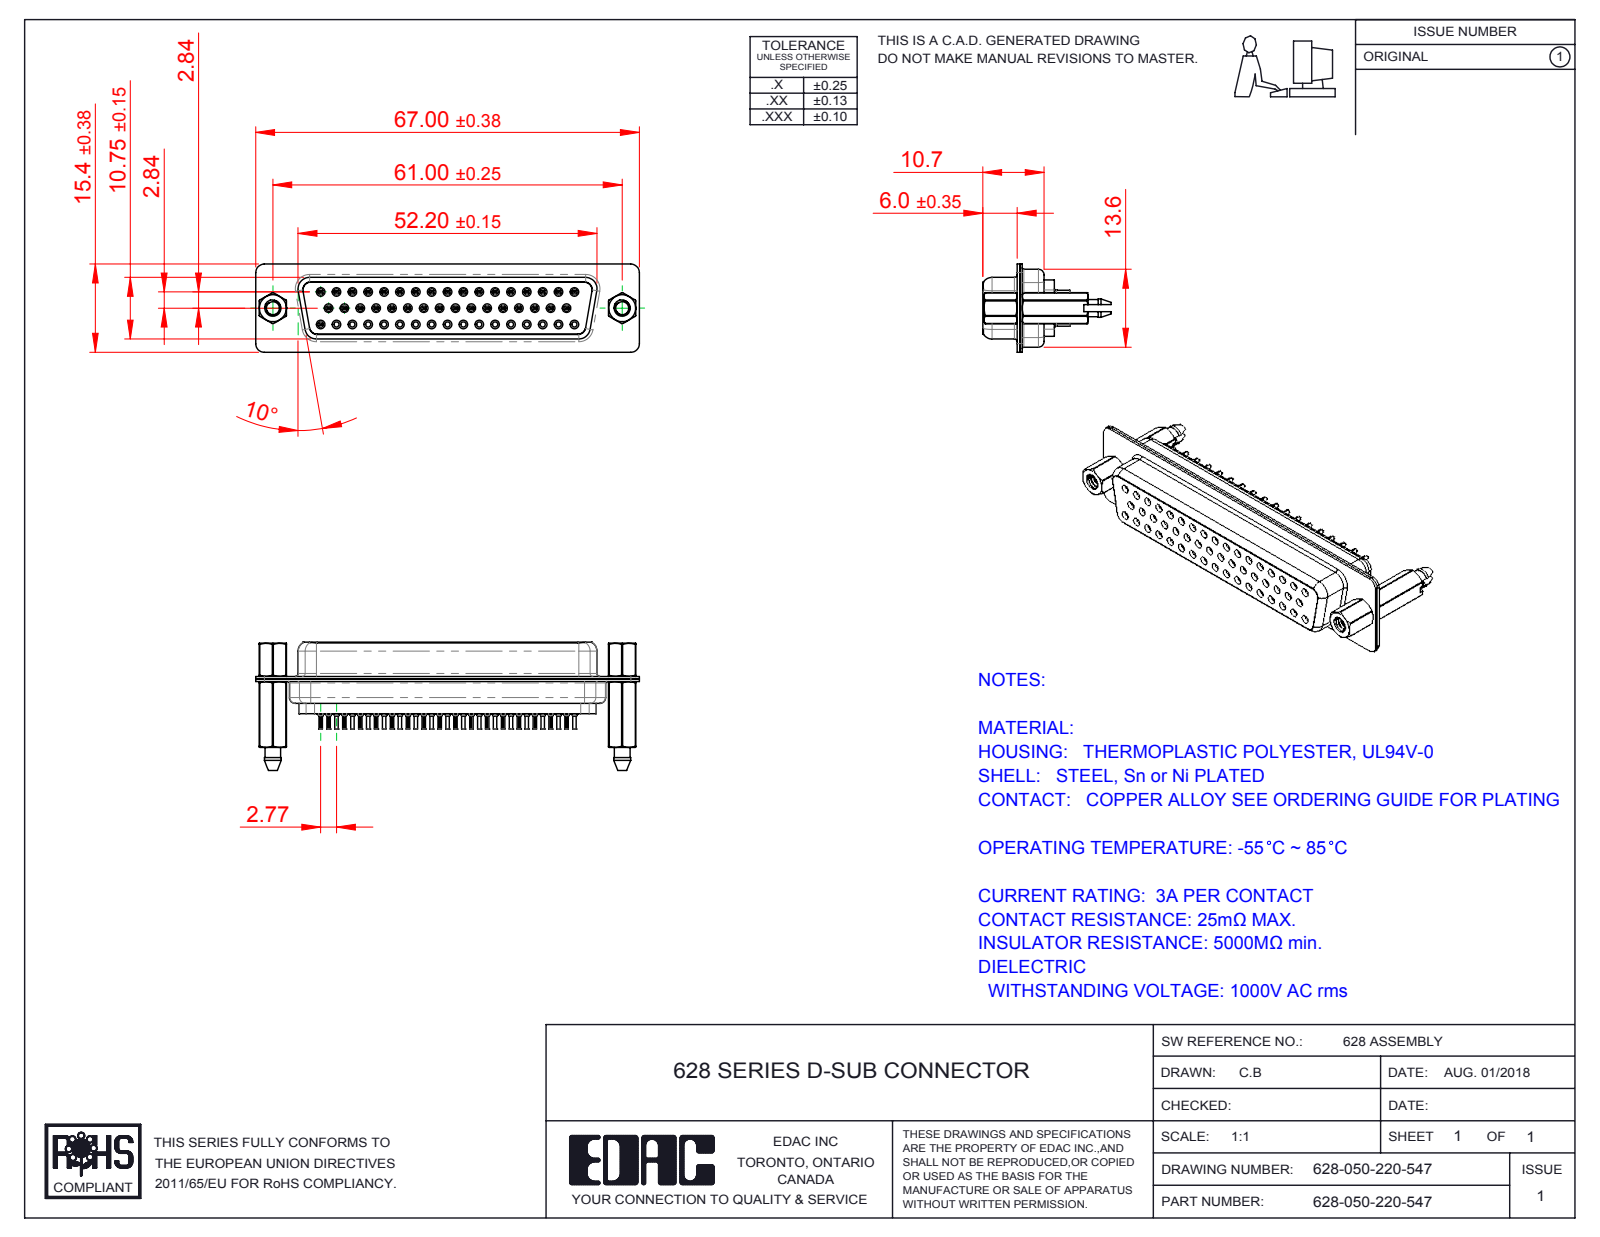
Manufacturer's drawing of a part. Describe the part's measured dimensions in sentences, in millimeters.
The part is named "628 Contact Row 3_20L; 628-050-220-547; 628 Contact Row 2_20L; 628 Housing_50 LP (+5 more)". Its 3-D file was written by "SolidWorks 2016 (CONFIG_CONTROL_DESIGN)". It is 41 solids with 5039 faces: 1223 planar, 1525 cylindrical and 2291 other. Overall it measures 67 by 22.4 by 15.4 millimeters. Its volume is 7 065 cubic millimeters and its surface area 14 684 square millimeters. Round holes: 50 of diameter 0.9, 50 of diameter 1.6, 34 of diameter 0.2, 34 of diameter 0.8, 34 of diameter 1.1, 17 of diameter 1.7, 16 of diameter 1.5, 16 of diameter 2, 2 of diameter 2.26, 2 of diameter 2.29, 2 of diameter 4, 2 of diameter 4.8. Round bosses or shafts: 34 of diameter 2, 34 of diameter 1.5, 34 of diameter 1.2, 34 of diameter 0.6, 2 of diameter 4.9, 2 of diameter 2.79. Partial cylindrical surfaces (rounded edges, fillets, slot ends): 68 of radius 0.1, 33 of radius 0.28, 18 of radius 1.5, 12 of radius 2, 8 of radius 1.35, 6 of radius 1.6, 4 of radius 0.25, 4 of radius 0.5. The main face-to-face distances are 0.45, 0.4, 10.3, 0.9, 6.05, 6.5, 6, 6.45, 12.5, 11.33. The hole center spacings are 3.16, 2.77, 5.54, 8.31, 11.08, 13.85, 16.62, 19.39.
